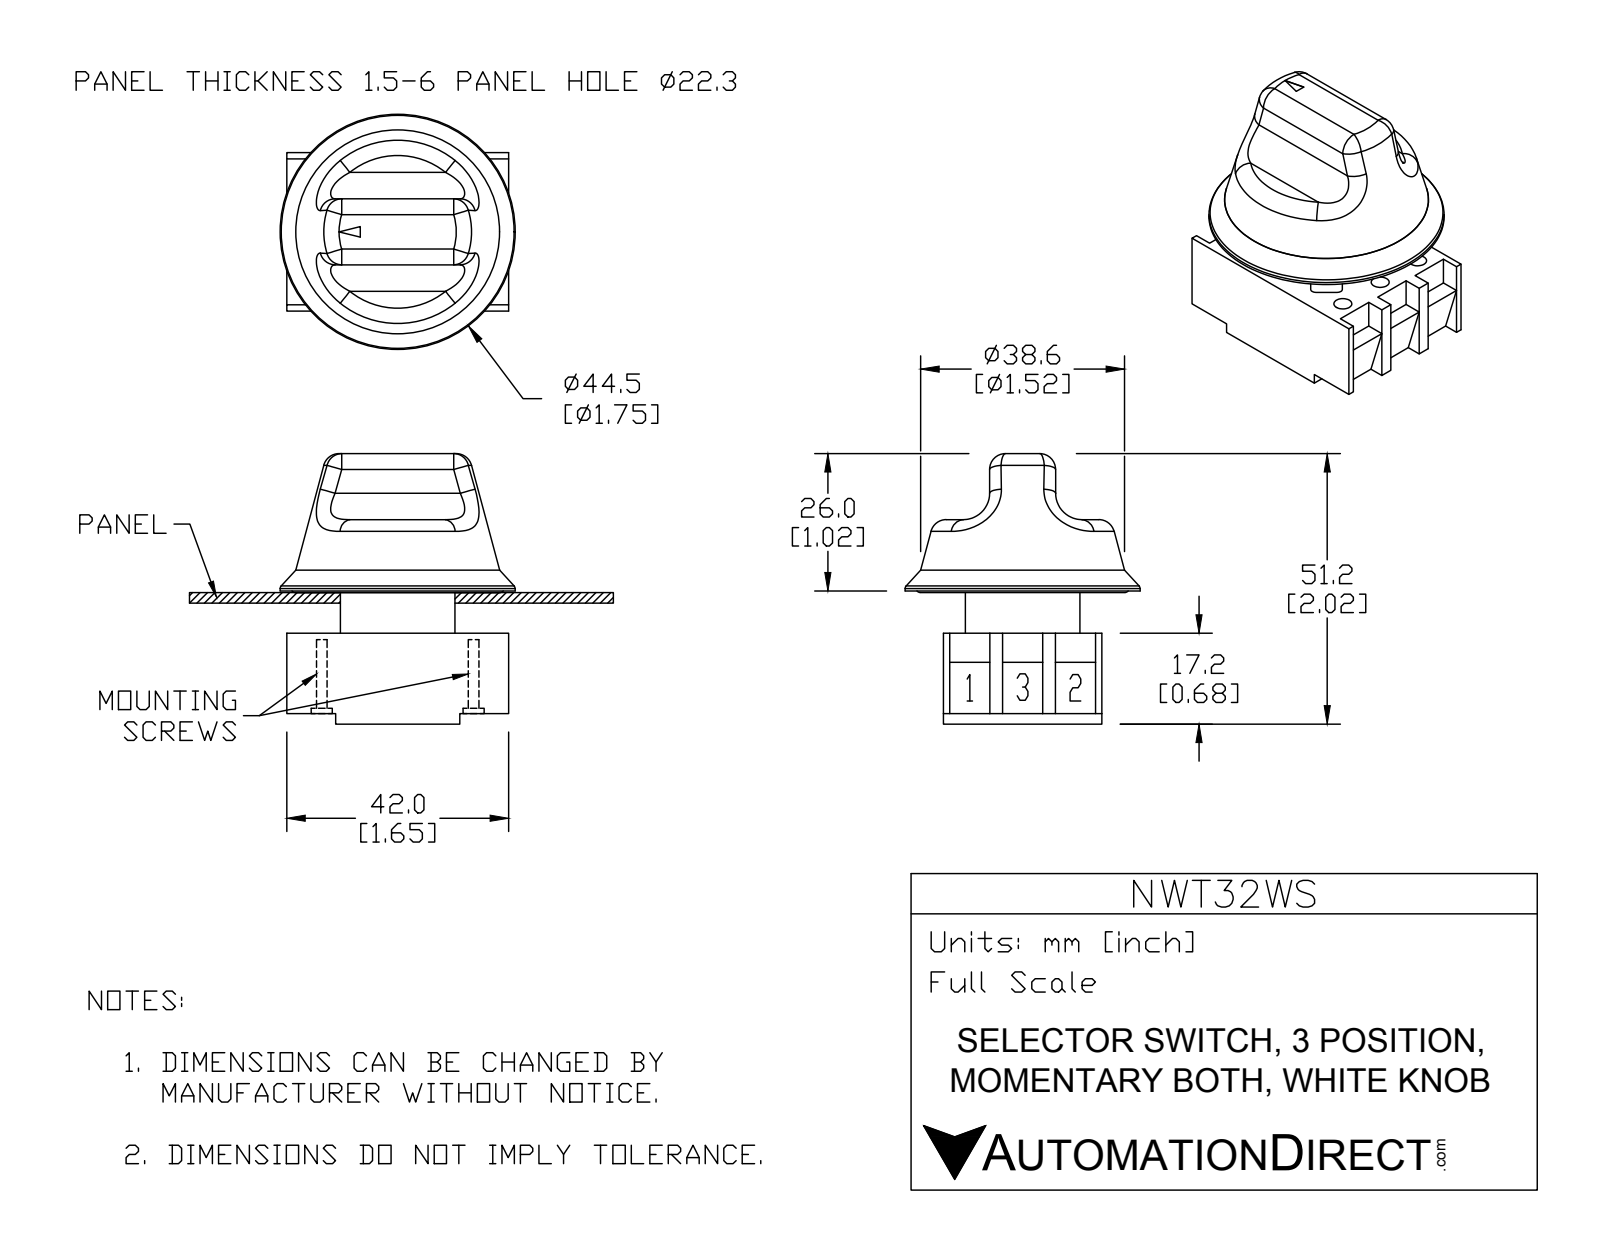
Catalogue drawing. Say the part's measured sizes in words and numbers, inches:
The part is named "NWT32WS". Its 3-D file was written by "SolidWorks 2015 (AUTOMOTIVE_DESIGN)". It is 7 solids with 236 faces: 134 planar, 67 cylindrical and 35 other. Overall it measures 2.016 by 1.752 by 1.752 inches. Its volume is 2.137 cubic inches and its surface area 29.6 square inches. Round holes: 6 of diameter 0.134, 6 of diameter 0.197, 1 of diameter 0.492. Round bosses or shafts: 2 of diameter 0.181, 2 of diameter 0.157, 1 of diameter 1.752, 1 of diameter 0.854. Partial cylindrical surfaces (rounded edges, fillets, slot ends): 8 of radius 0.039, 5 of radius 0.343, 2 of radius 0.118, 2 of radius 0.197, 1 of radius 0.433. The main face-to-face distances are 0.156, 1.181, 0.315, 0.47, 0.303, 0.167, 0.394, 0.598, 0.902, 0.913. The hole center spacings are 0.394, 0.69, 1.199, 1.132, 0.566, 0.787, 1.379.
